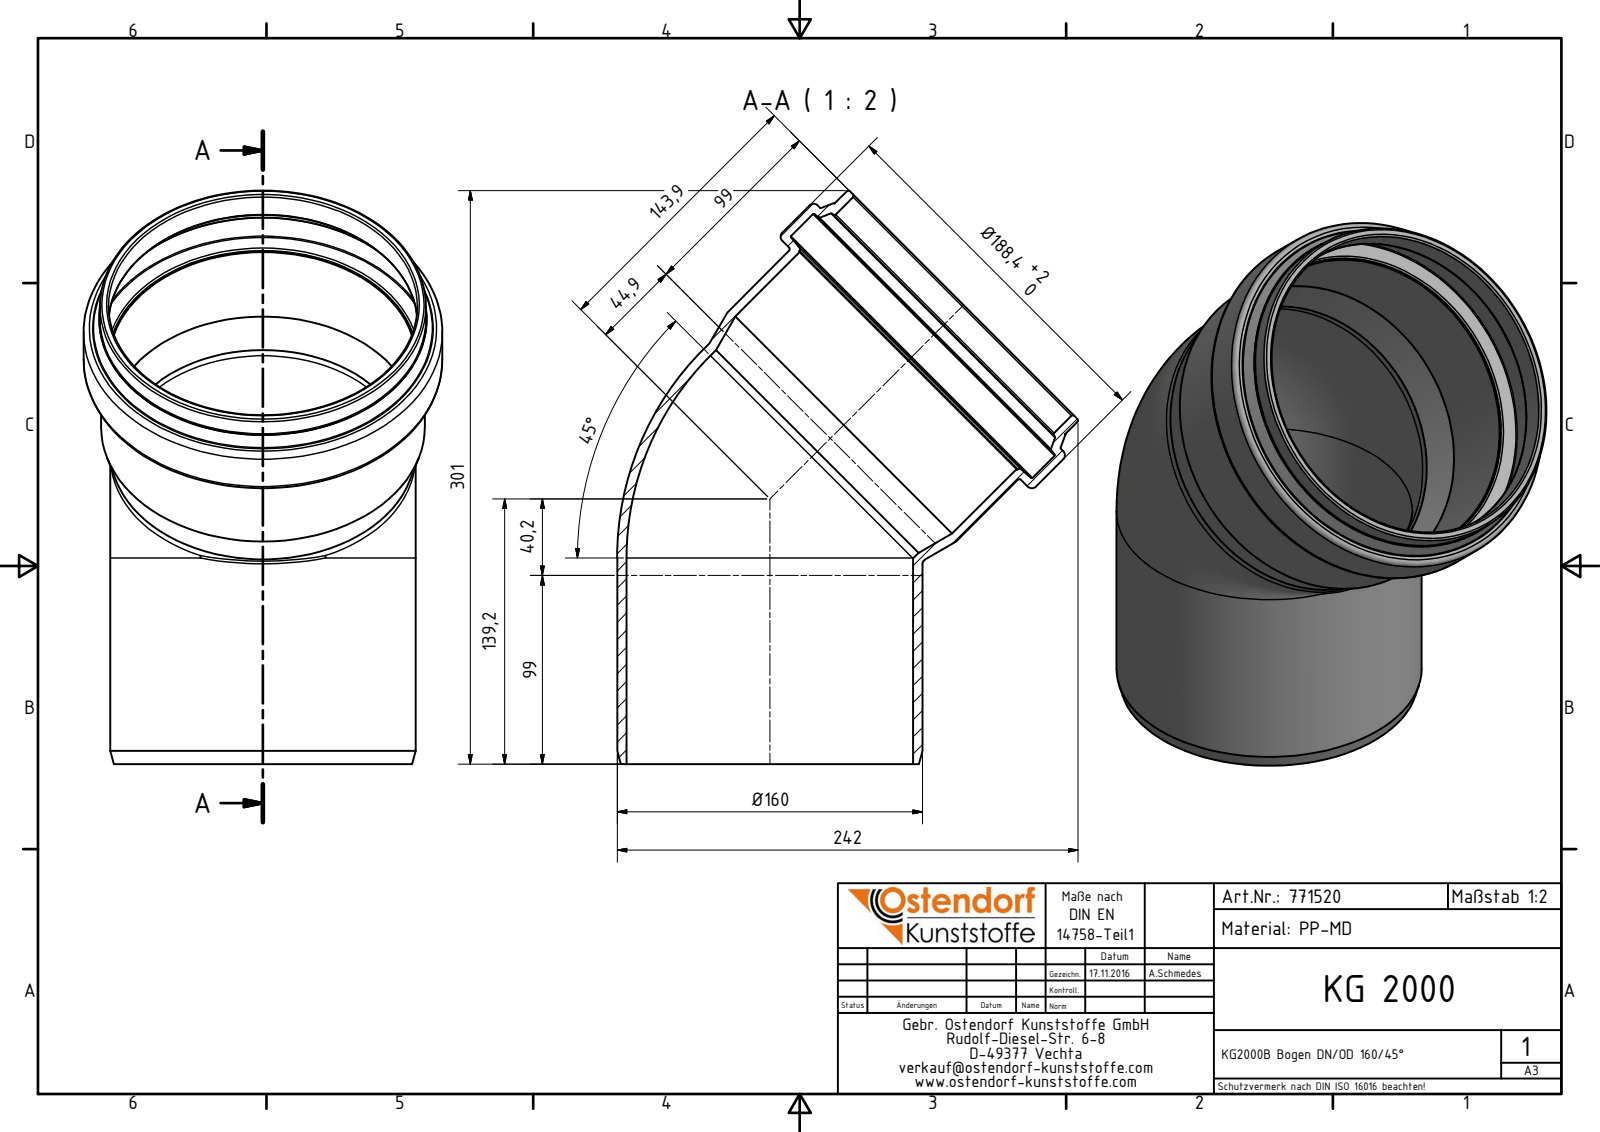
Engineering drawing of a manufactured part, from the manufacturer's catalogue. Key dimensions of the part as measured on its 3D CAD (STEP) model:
Part name (STEP PRODUCT): 771520 KG2000B Bogen DN_OD 160_45°
STEP written by: Autodesk Inventor 2016 (AUTOMOTIVE_DESIGN)
Units: millimetres
Bodies: 1 solid, 42 faces (6 planar, 11 cylindrical, 25 other)
Overall size (bounding box): 301 × 242 × 188.4
Volume: 667 855 mm³ · Surface area: 300 767 mm²
Round holes (diameter × count): ⌀150.5 ×2, ⌀162.2 ×2, ⌀161 ×1, ⌀179.4 ×1
Round bosses / shafts (diameter × count): ⌀160.3 ×2, ⌀188.4 ×1, ⌀171.2 ×1, ⌀170 ×1
Main face-to-face distances: 43.49, 26.3, 17.19, 2.29, 24.01, 41.2, 33.2, 30.91, 6.9, 10.29
